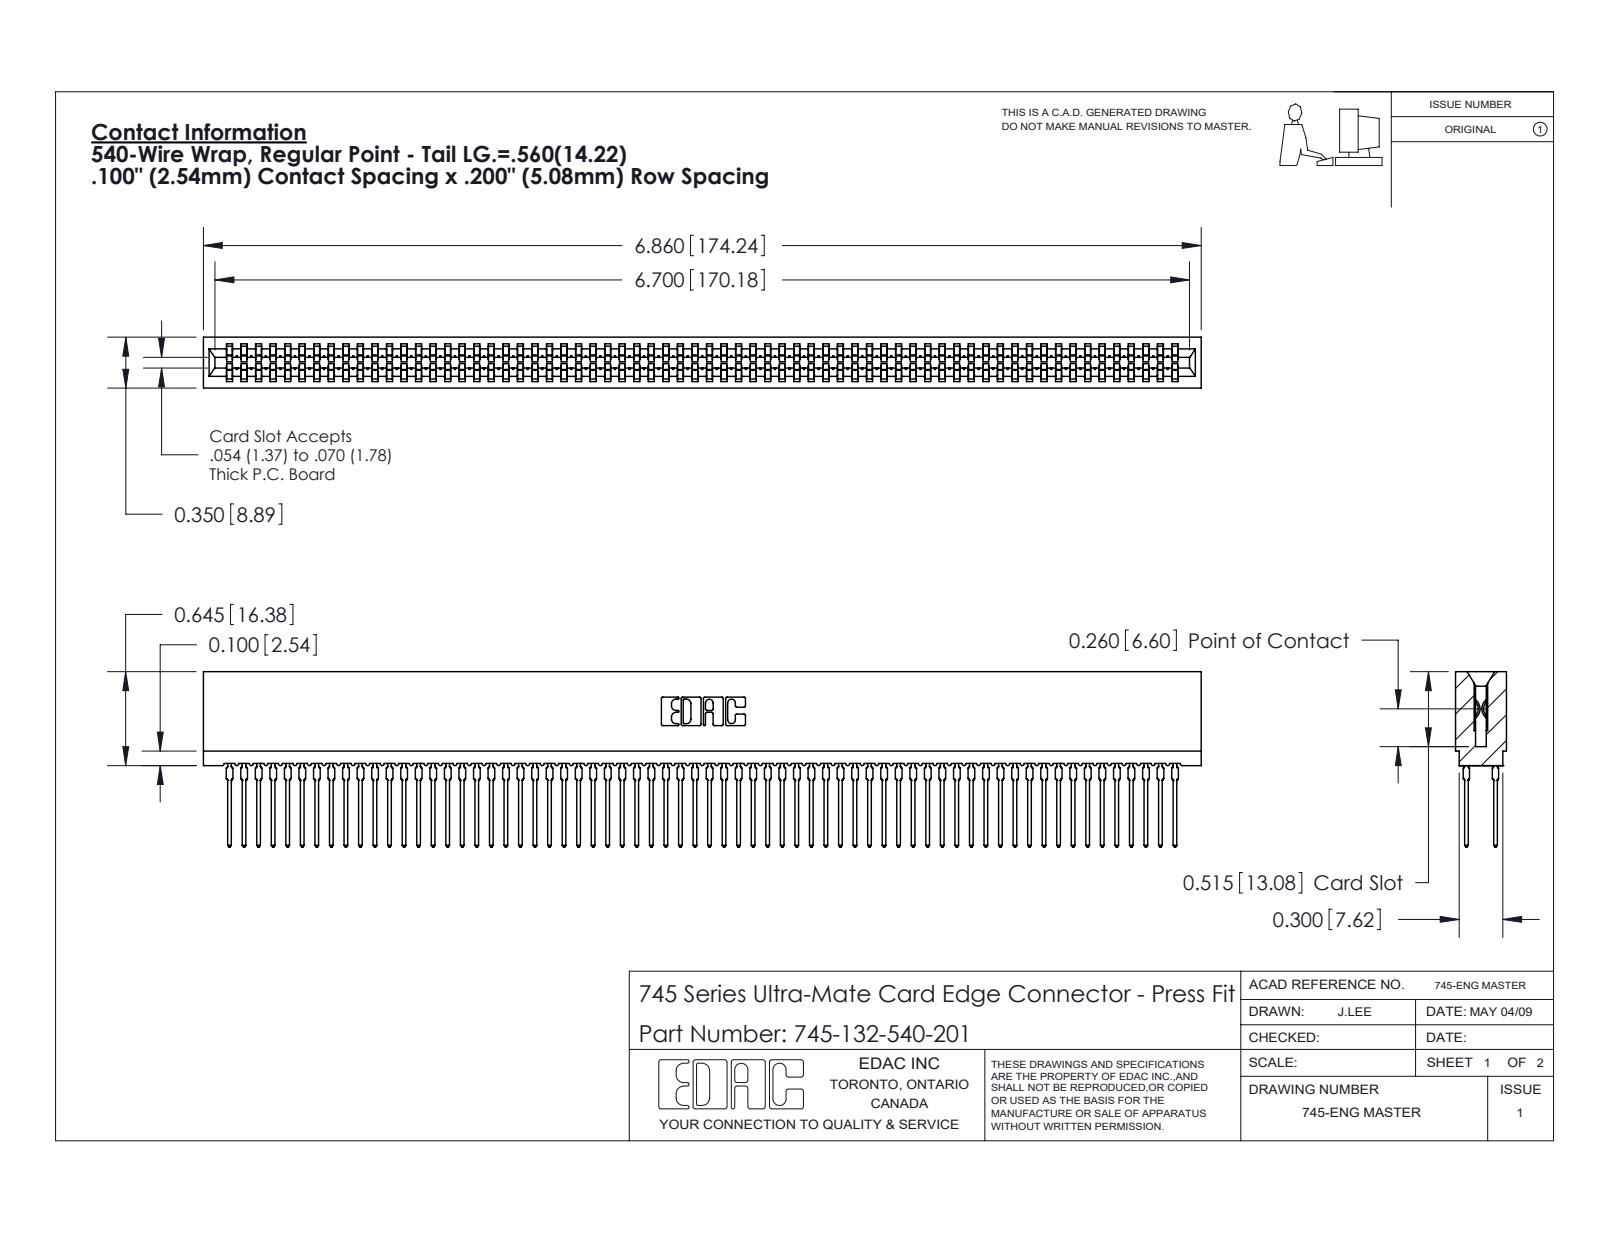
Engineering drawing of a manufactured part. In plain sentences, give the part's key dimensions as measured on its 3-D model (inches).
The part is named "745-292-001_540; 745 Part_Insulator Option - 01; 745-132-540-201". Its 3-D file was written by "SolidWorks 2020 (CONFIG_CONTROL_DESIGN)". It is 133 solids with 11909 faces: 6127 planar, 2350 cylindrical and 3432 other. Overall it measures 6.86 by 1.206 by 0.35 inches. Its volume is 0.973 cubic inches and its surface area 53.44 square inches. Partial cylindrical surfaces (rounded edges, fillets, slot ends): 264 of radius 0.021, 132 of radius 0.015, 22 of radius 0.01, 8 of radius 0.005, 8 of radius 0.011, 6 of radius 0.007, 6 of radius 0.031, 3 of radius 0.026. The main face-to-face distances are 0.063, 0.287, 0.35, 0.2, 0.045, 0.305, 0.018, 0.243, 0.138, 0.212.
